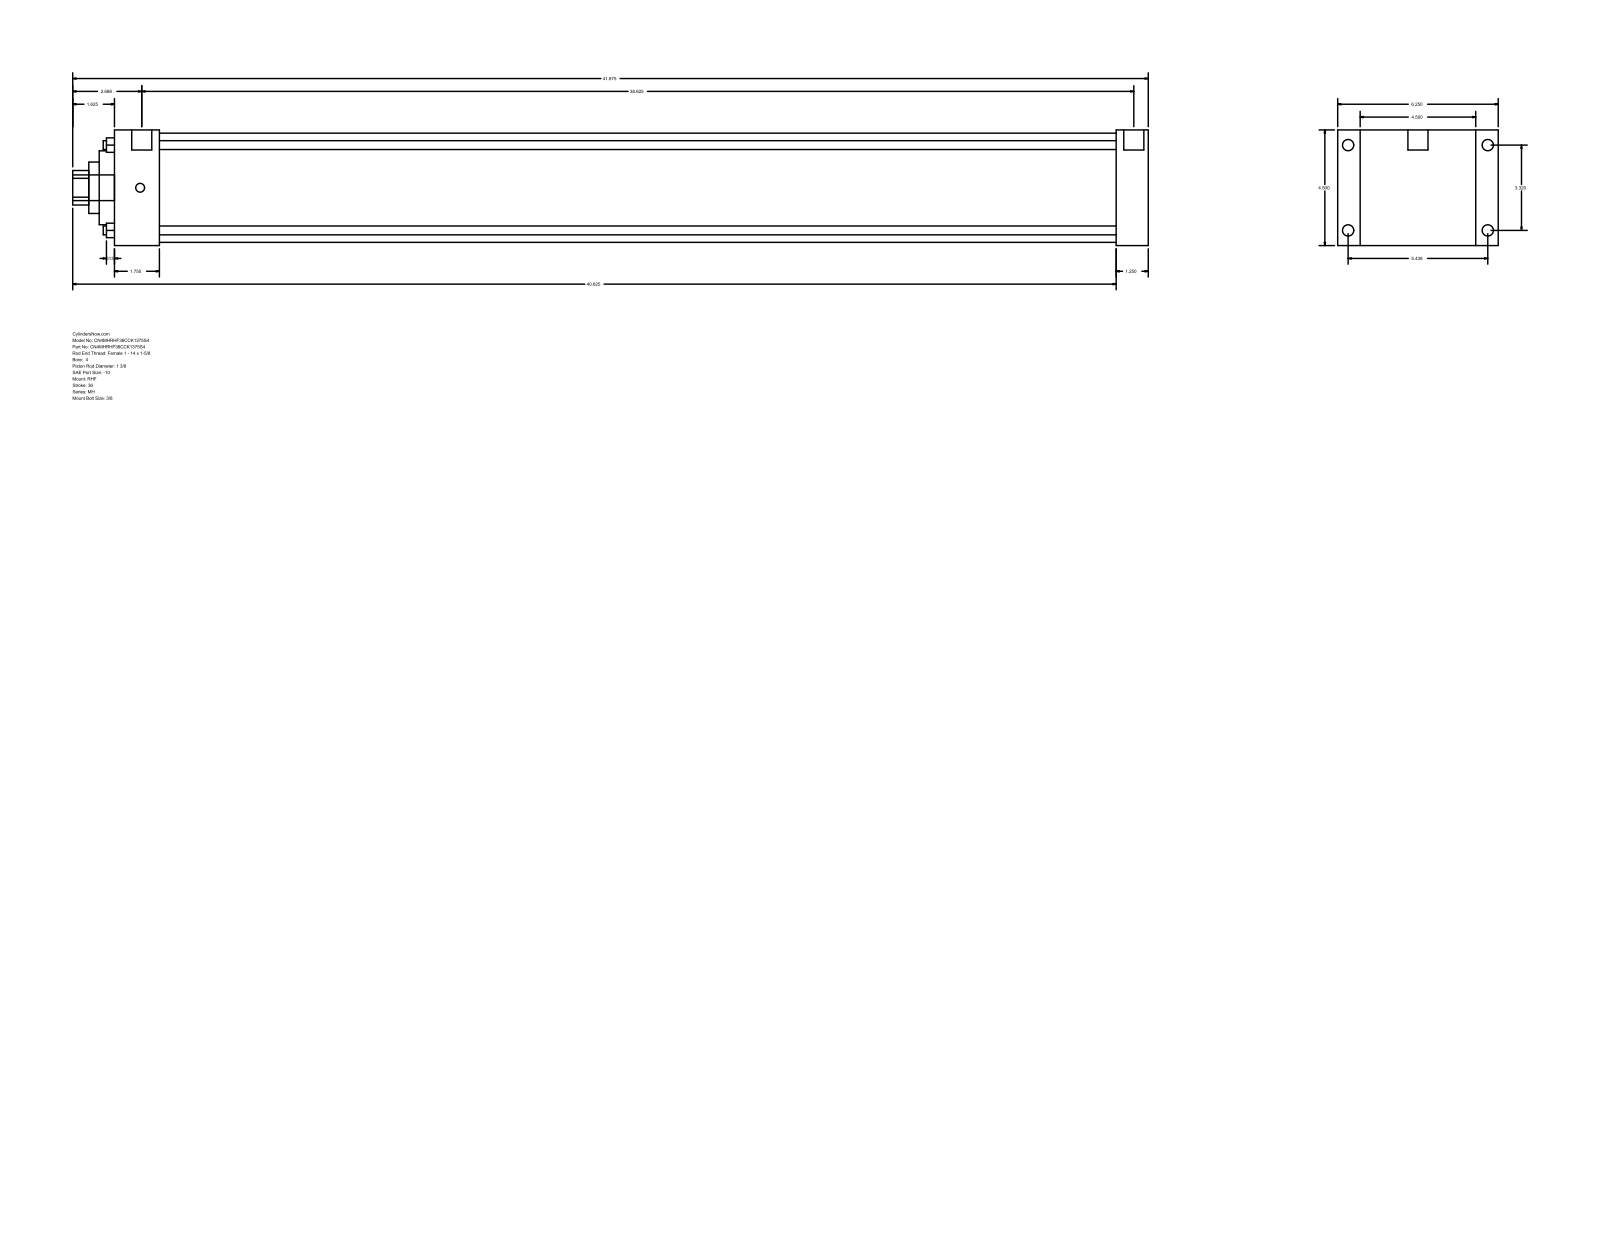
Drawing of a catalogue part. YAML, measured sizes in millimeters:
part_name: "MH_RHF__0400_1.375"
step_written_by: "GSSL Pune (CONFIG_CONTROL_DESIGN)"
units: millimeters
bodies: {solids: 0, faces: 90, planar: 61, cylindrical: 29, other: 0}
overall_size: [1063.62, 158.75, 114.3]
round_holes:
  - {diameter: 8.76, count: 4}
  - {diameter: 34.92, count: 1}
  - {diameter: 50.8, count: 1}
  - {diameter: 73.03, count: 1}
  - {diameter: 107.95, count: 1}
round_bosses_or_shafts:
  - {diameter: 11.13, count: 4}
  - {diameter: 8.73, count: 4}
  - {diameter: 19.84, count: 2}
  - {diameter: 25.4, count: 1}
partial_cylinders:
  - {radius: 17.06, count: 1}
face_to_face_distances: [114.3, 1022.35, 990.61, 31.74, 22.23, 136.53, 44.45, 946.16, 977.9, 158.76]
hole_center_spacings: [59.62, 84.32, 119.25]
